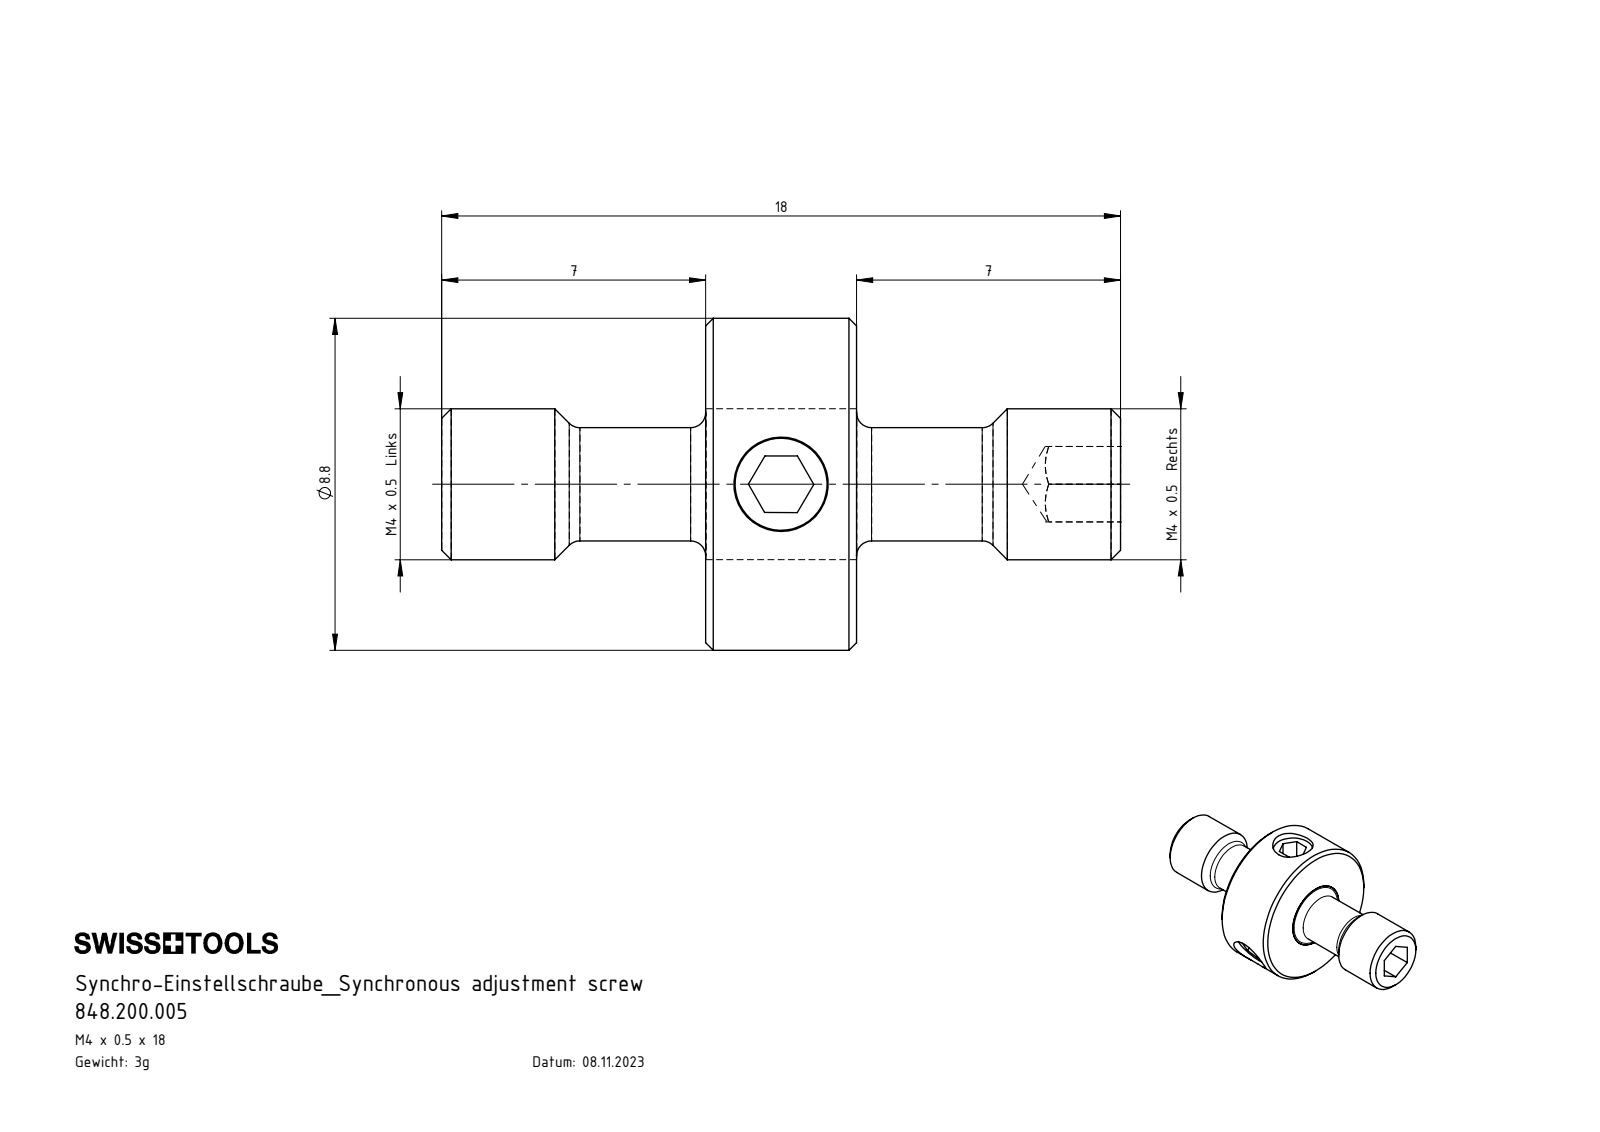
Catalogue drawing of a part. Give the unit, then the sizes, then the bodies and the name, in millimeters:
Units: millimetres
Overall size (bounding box): 18 × 8.8 × 8.8
Round holes (diameter × count): ⌀2.5 ×3
Round bosses / shafts (diameter × count): ⌀3 ×4, ⌀8.8 ×1, ⌀4 ×1
Main face-to-face distances: 4, 7, 11, 1.5, 2, 18
Volume: 360 mm³ · Surface area: 636 mm²
Bodies: 5 solids, 96 faces (36 planar, 26 cylindrical, 34 other)
Part name (STEP PRODUCT): Z20-ER3.002.004_A; ISO 4026 - M3 x 2; 848.200.005; Z20-ER3.001.018_A
STEP written by: SolidWorks 2022 (AUTOMOTIVE_DESIGN)
